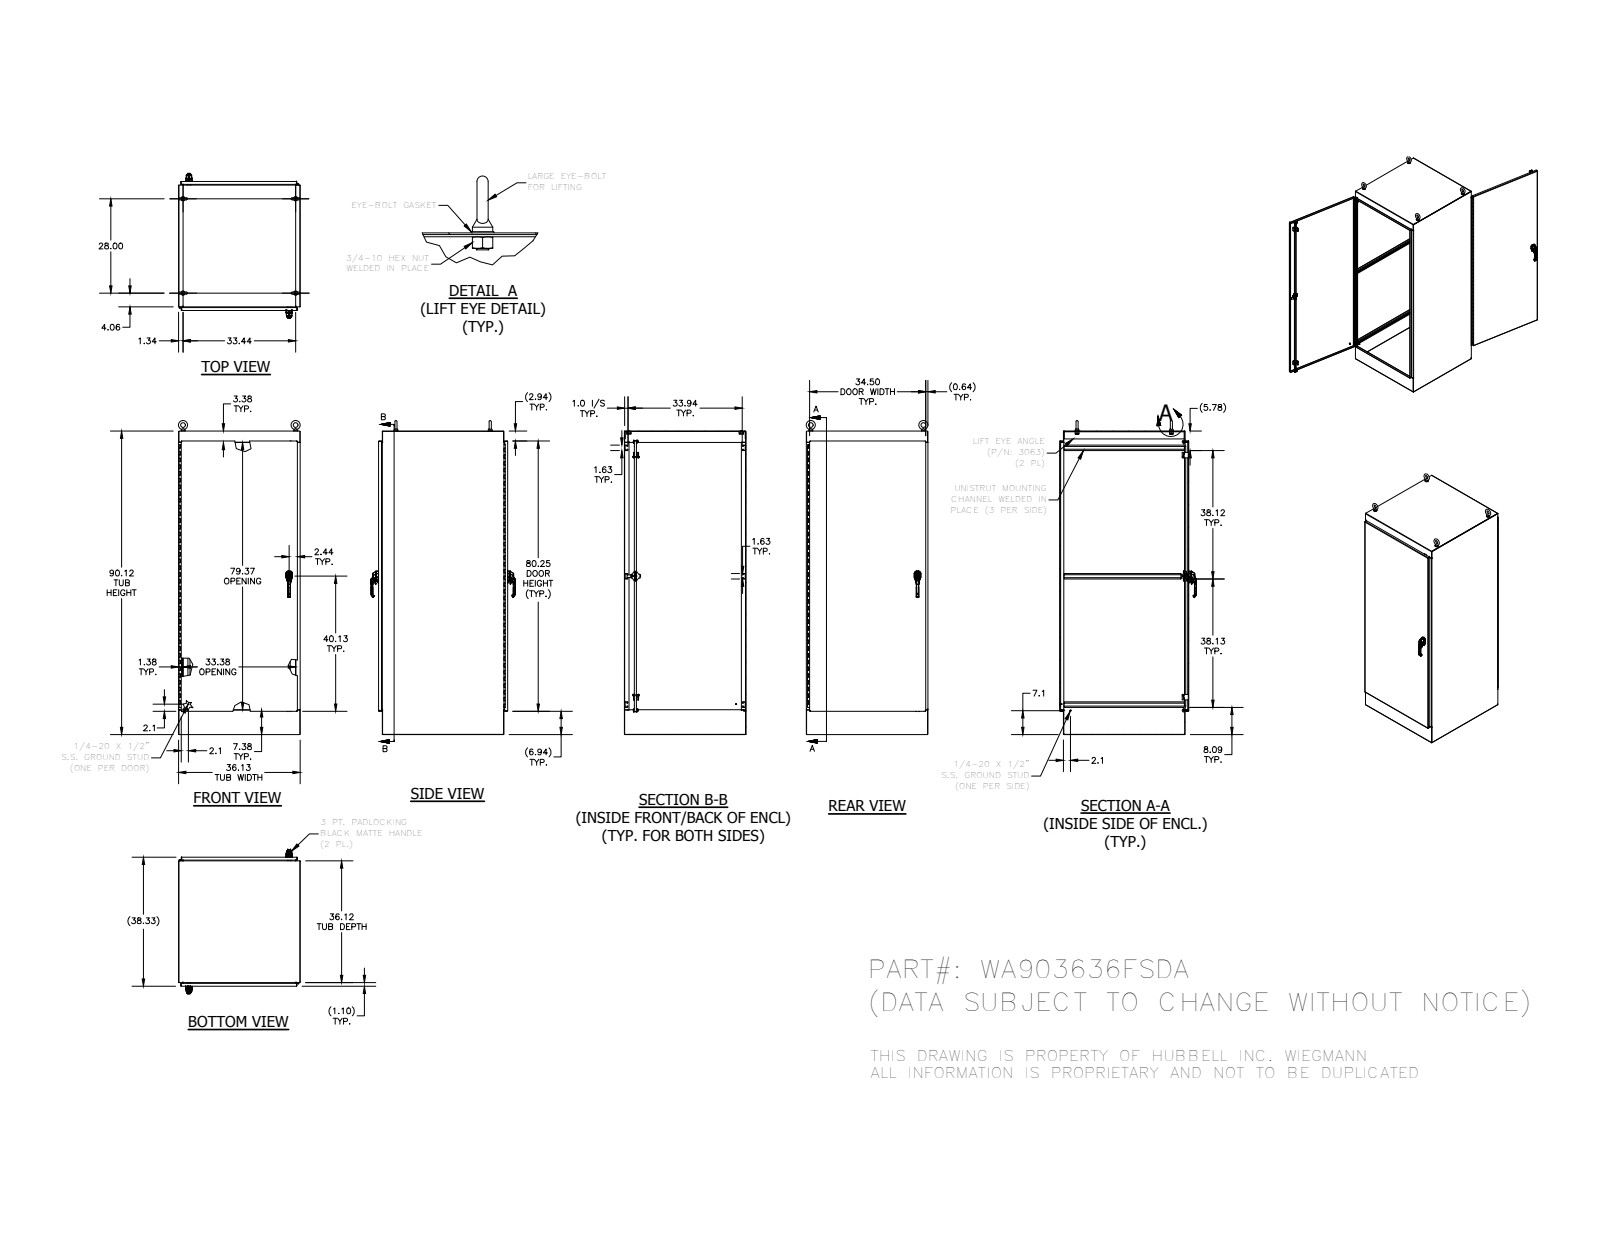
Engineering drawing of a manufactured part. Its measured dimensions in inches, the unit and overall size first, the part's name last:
Units: inches
Overall size (bounding box): 93.248 × 42.871 × 36.125
Round holes (diameter × count): ⌀0.276 ×16, ⌀0.375 ×16, ⌀0.2 ×8, ⌀0.213 ×6, ⌀0.236 ×6, ⌀0.28 ×6, ⌀0.241 ×4, ⌀0.25 ×4, ⌀0.252 ×4, ⌀0.4 ×4, ⌀0.407 ×4, ⌀0.413 ×4
Round bosses / shafts (diameter × count): ⌀1.25 ×4, ⌀1.12 ×4, ⌀1 ×4, ⌀0.75 ×4, ⌀0.563 ×4, ⌀0.526 ×4, ⌀0.5 ×4, ⌀0.375 ×4
Partial cylindrical surfaces — rounded edges, fillets, slot ends (radius × count): R0.02 ×333, R0.012 ×174, R0.019 ×38, R0.01 ×32, R0.079 ×30, R0.05 ×28, R0.031 ×26, R0.118 ×24
Main face-to-face distances: 0.094, 36.031, 0.125, 38.209, 35.938, 36.125, 38.084, 38.334, 90.031, 89.937
Hole centre spacings: 35.33, 38.386, 26, 43.001, 8.667, 17.333, 34.25, 8.667
Volume: 1 917 in³ · Surface area: 37 290 in²
Bodies: 90 solids, 5748 faces (2382 planar, 2010 cylindrical, 1356 other)
Part name (STEP PRODUCT): WA9036FSDALRS; WA3636FSDABTM; WA3636FSDATOP; WA9036FSDADR (+8 more)
STEP written by: Autodesk Inventor 2014 (AUTOMOTIVE_DESIGN)
